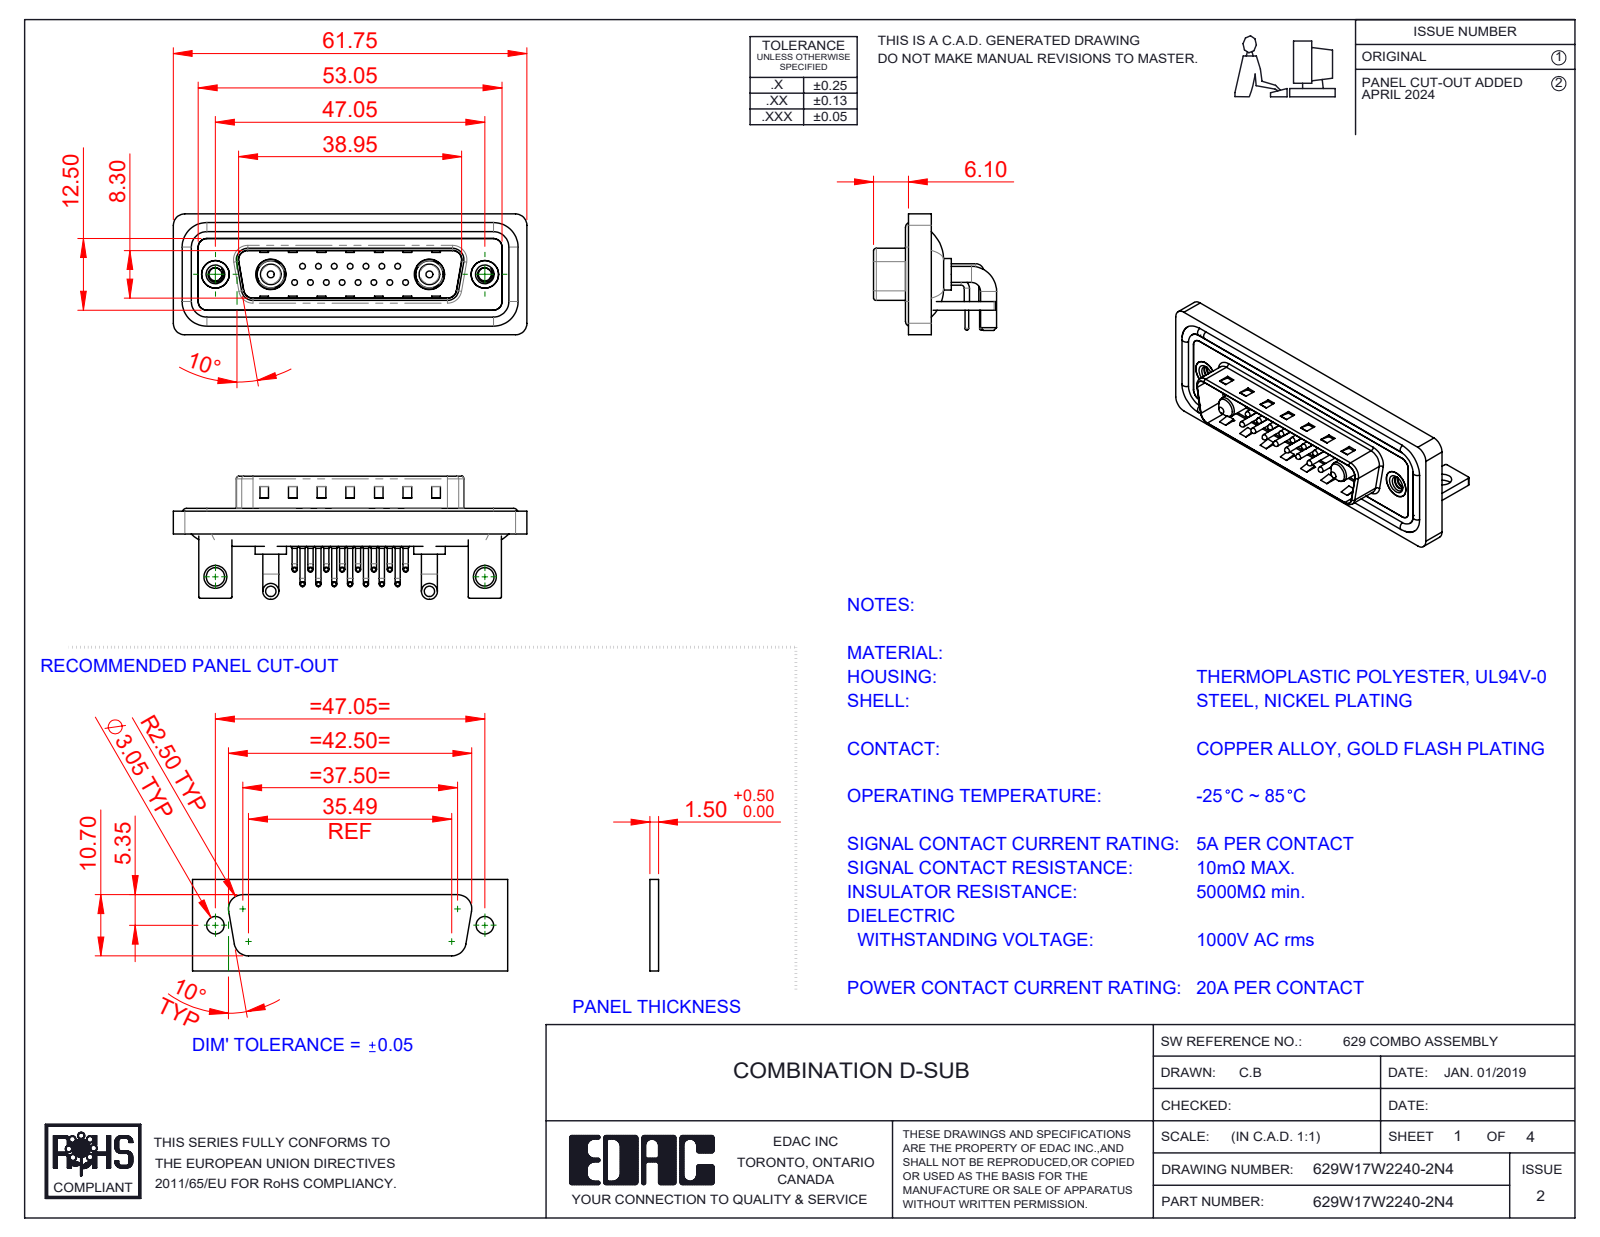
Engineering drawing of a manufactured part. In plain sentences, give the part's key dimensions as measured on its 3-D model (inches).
The part is named "Power Pin_20A RA; 629Combo Stabilizer Bracket; 629Combo Contact Row 2; 629Combo Housing_17W2 (+6 more)". Its 3-D file was written by "SolidWorks 2023 (CONFIG_CONTROL_DESIGN)". It is 28 solids with 2259 faces: 1209 planar, 788 cylindrical and 262 other. Overall it measures 2.431 by 0.846 by 0.831 inches. Its volume is 0.475 cubic inches and its surface area 20.44 square inches. Round holes: 15 of diameter 0.03, 15 of diameter 0.063, 15 of diameter 0.079, 2 of diameter 0.089, 2 of diameter 0.126, 2 of diameter 0.157, 2 of diameter 0.189, 2 of diameter 0.191, 2 of diameter 0.197, 2 of diameter 0.209. Round bosses or shafts: 30 of diameter 0.035, 15 of diameter 0.059, 15 of diameter 0.039, 15 of diameter 0.026, 4 of diameter 0.11, 4 of diameter 0.063, 2 of diameter 0.217, 2 of diameter 0.205. Partial cylindrical surfaces (rounded edges, fillets, slot ends): 19 of radius 0.079, 18 of radius 0.059, 16 of radius 0.01, 15 of radius 0.04, 9 of radius 0.02, 8 of radius 0.063, 4 of radius 0.024, 4 of radius 0.026. The main face-to-face distances are 0.016, 0.031, 0.059, 0.083, 0.114, 0.043, 0.161, 0.063, 0.177, 0.146. The hole center spacings are 0.124, 0.109, 0.218, 0.327, 0.198, 0.295, 0.436, 0.198.
